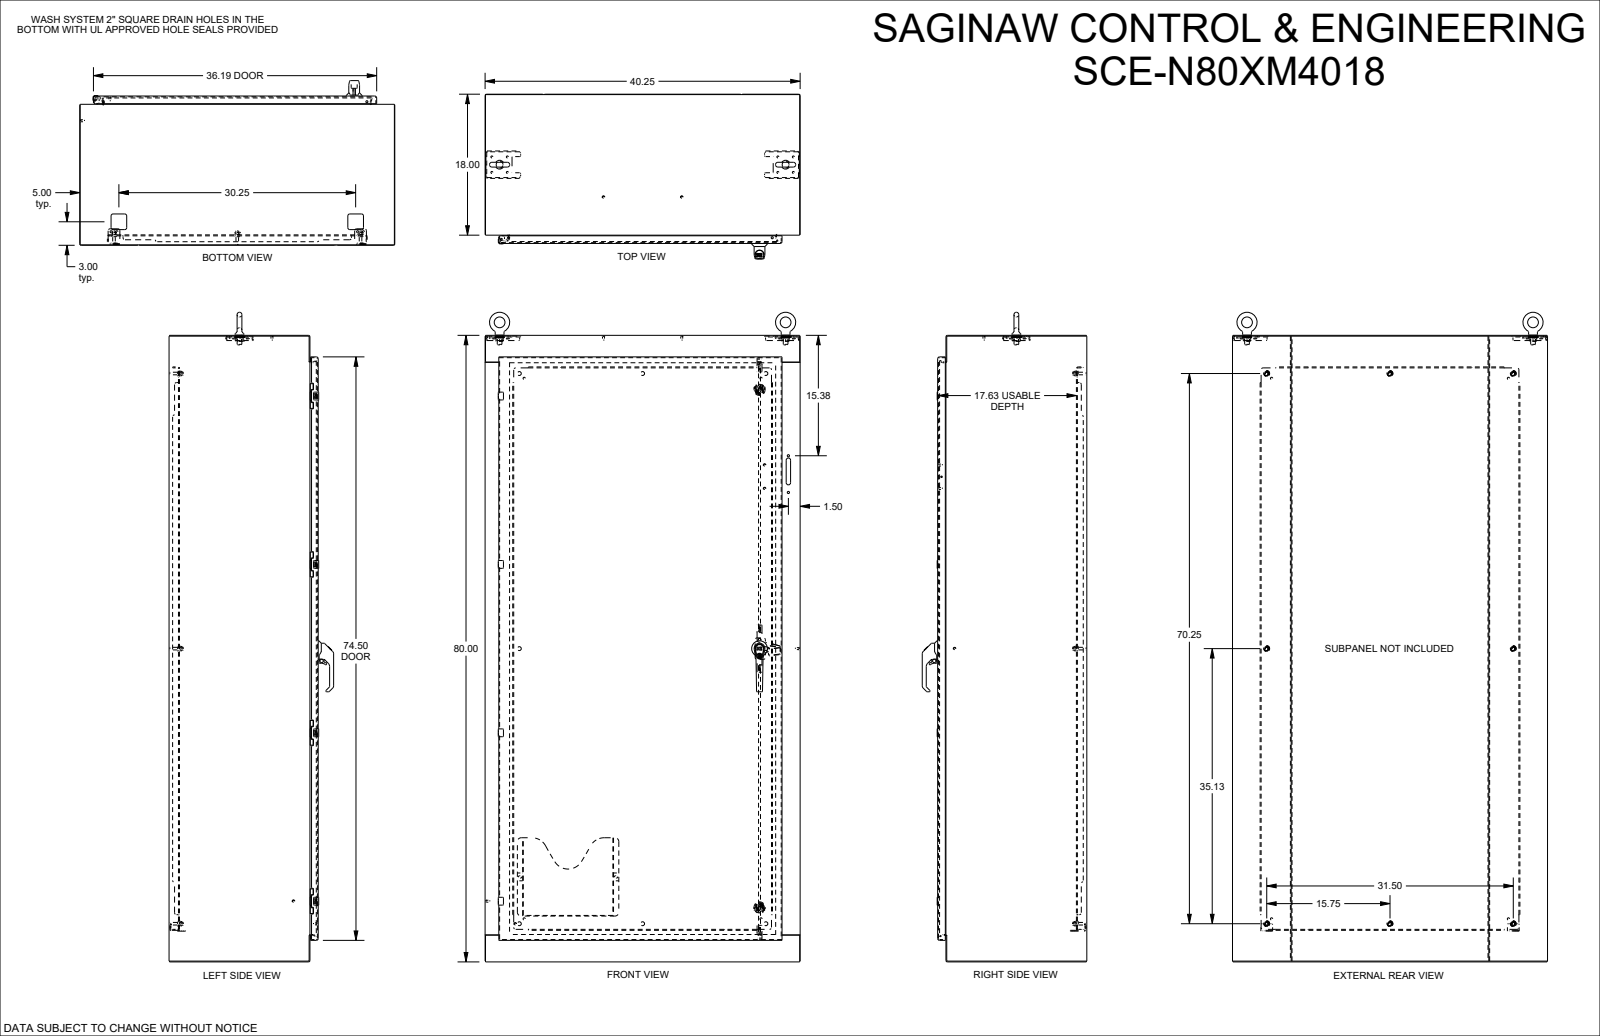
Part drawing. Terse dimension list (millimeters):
name: SCE-N80XM4018
written by: SolidWorks 2023 (AUTOMOTIVE_DESIGN)
unit: mm
bodies: 23 solids, 3153 faces (1334 planar, 1027 cylindrical, 792 other)
size: 2106.8 × 1022.4 × 534.6
volume: 20 070 000 mm³; area: 15 120 000 mm²
holes: 10× ⌀6.4, 8× ⌀5.2, 8× ⌀6.2, 8× ⌀9.5, 4× ⌀1, 4× ⌀4.3, 4× ⌀5.5, 4× ⌀6.5, 2× ⌀7.1, 2× ⌀8.7, 2× ⌀9.1, 2× ⌀22.2
bosses: 12× ⌀4.3, 8× ⌀6.4, 8× ⌀6.1, 5× ⌀5, 2× ⌀35.6, 2× ⌀29.8, 2× ⌀15.2, 2× ⌀8.7
rounds: 96× R0.8, 68× R0.4, 37× R1, 31× R3.2, 24× R0.5, 24× R1.6, 22× R1, 21× R2
face distances: 2.6, 481.4, 2.6, 1019.7, 478.8, 484.1, 454.6, 26.9, 1022.4, 2029.4
hole spacings: 546.1, 1092.2, 12.5, 12.5, 25, 35.5, 35.6, 50.3
